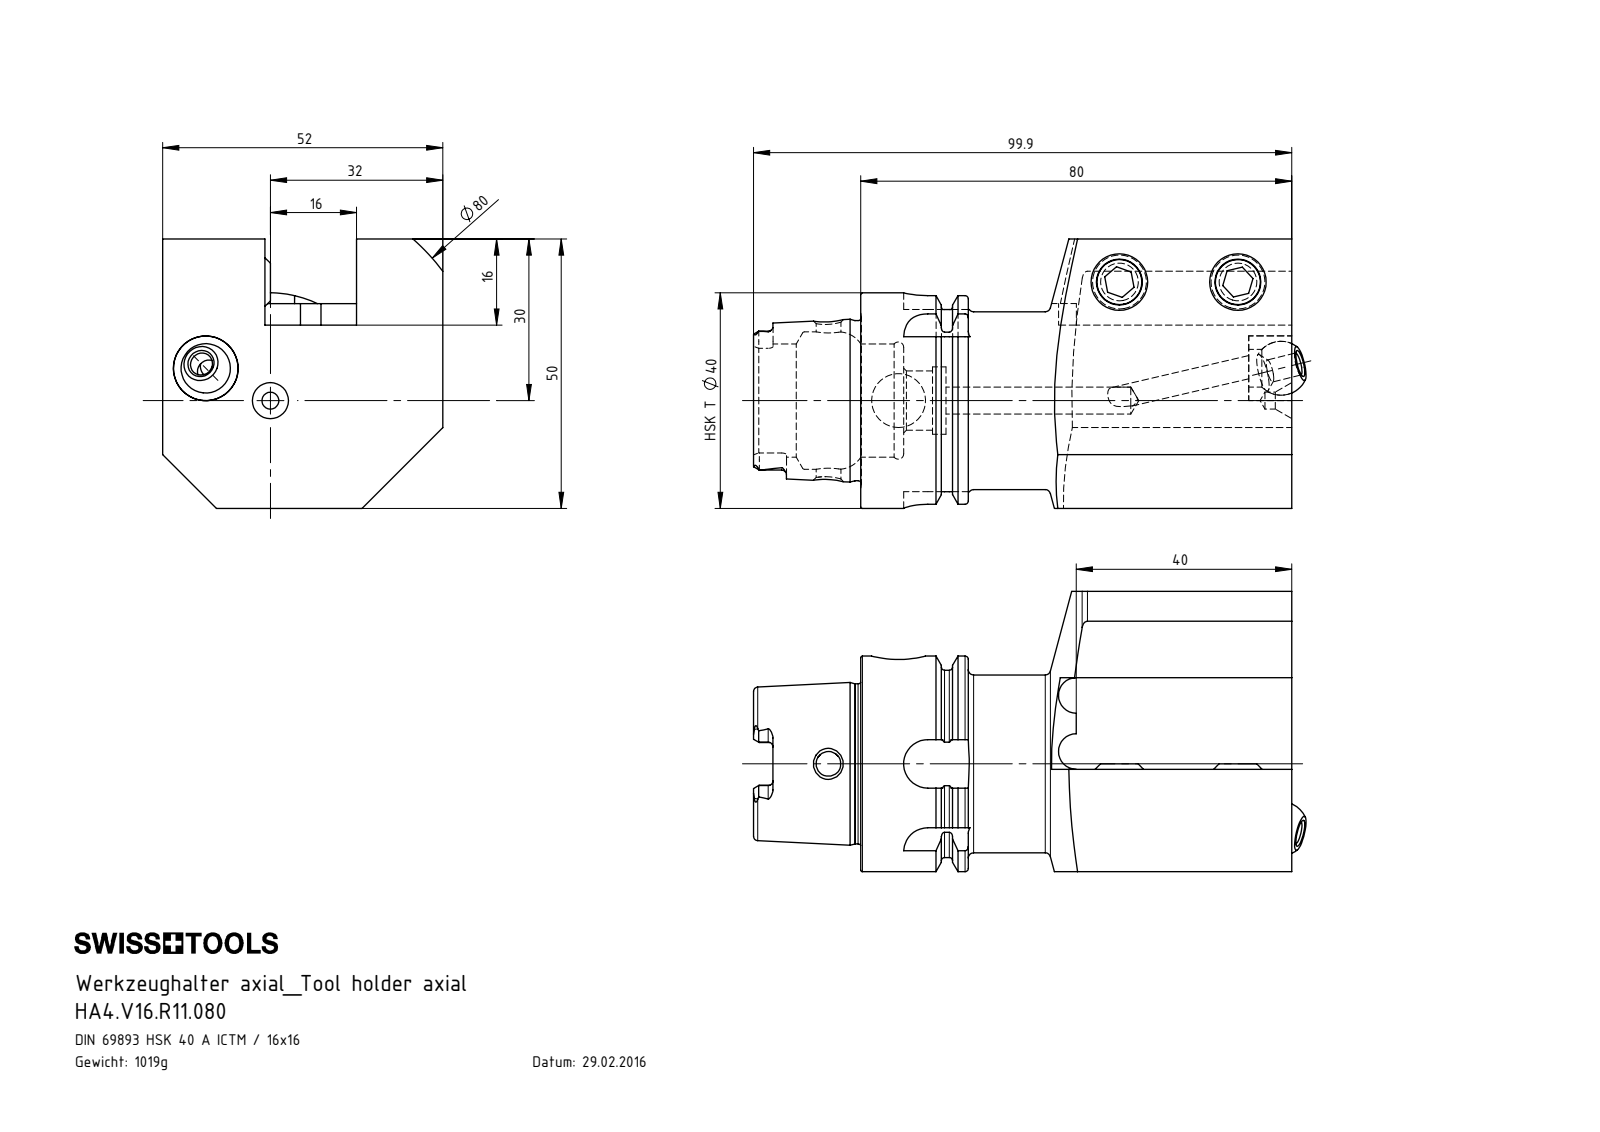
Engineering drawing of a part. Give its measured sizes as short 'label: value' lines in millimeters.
name: KU1-U12.001.010_1; HA4-V16.R11.080_A_Fertigbearbeitung; ISO 4026 - M10 x 18; HA4.V16.R11.080 (+2 more)
written by: SolidWorks 2017 (AUTOMOTIVE_DESIGN)
unit: mm
bodies: 5 solids, 185 faces (80 planar, 45 cylindrical, 60 other)
size: 101.7 × 52 × 50
volume: 130 098 mm³; area: 27 484 mm²
holes: 2× ⌀4.2, 2× ⌀8.5, 1× ⌀3.15, 1× ⌀4.6, 1× ⌀5, 1× ⌀7, 1× ⌀10, 1× ⌀11, 1× ⌀12, 1× ⌀12.5, 1× ⌀21, 1× ⌀25.5
bosses: 2× ⌀10, 1× ⌀40, 1× ⌀34.75, 1× ⌀33, 1× ⌀29.71
rounds: 6× R0.9, 4× R1.88, 4× R4.5, 2× R3.3, 1× R40
face distances: 16, 50, 52, 34, 36, 17, 33, 19, 80, 12
hole spacings: 13.42, 22, 46.53, 66.73
